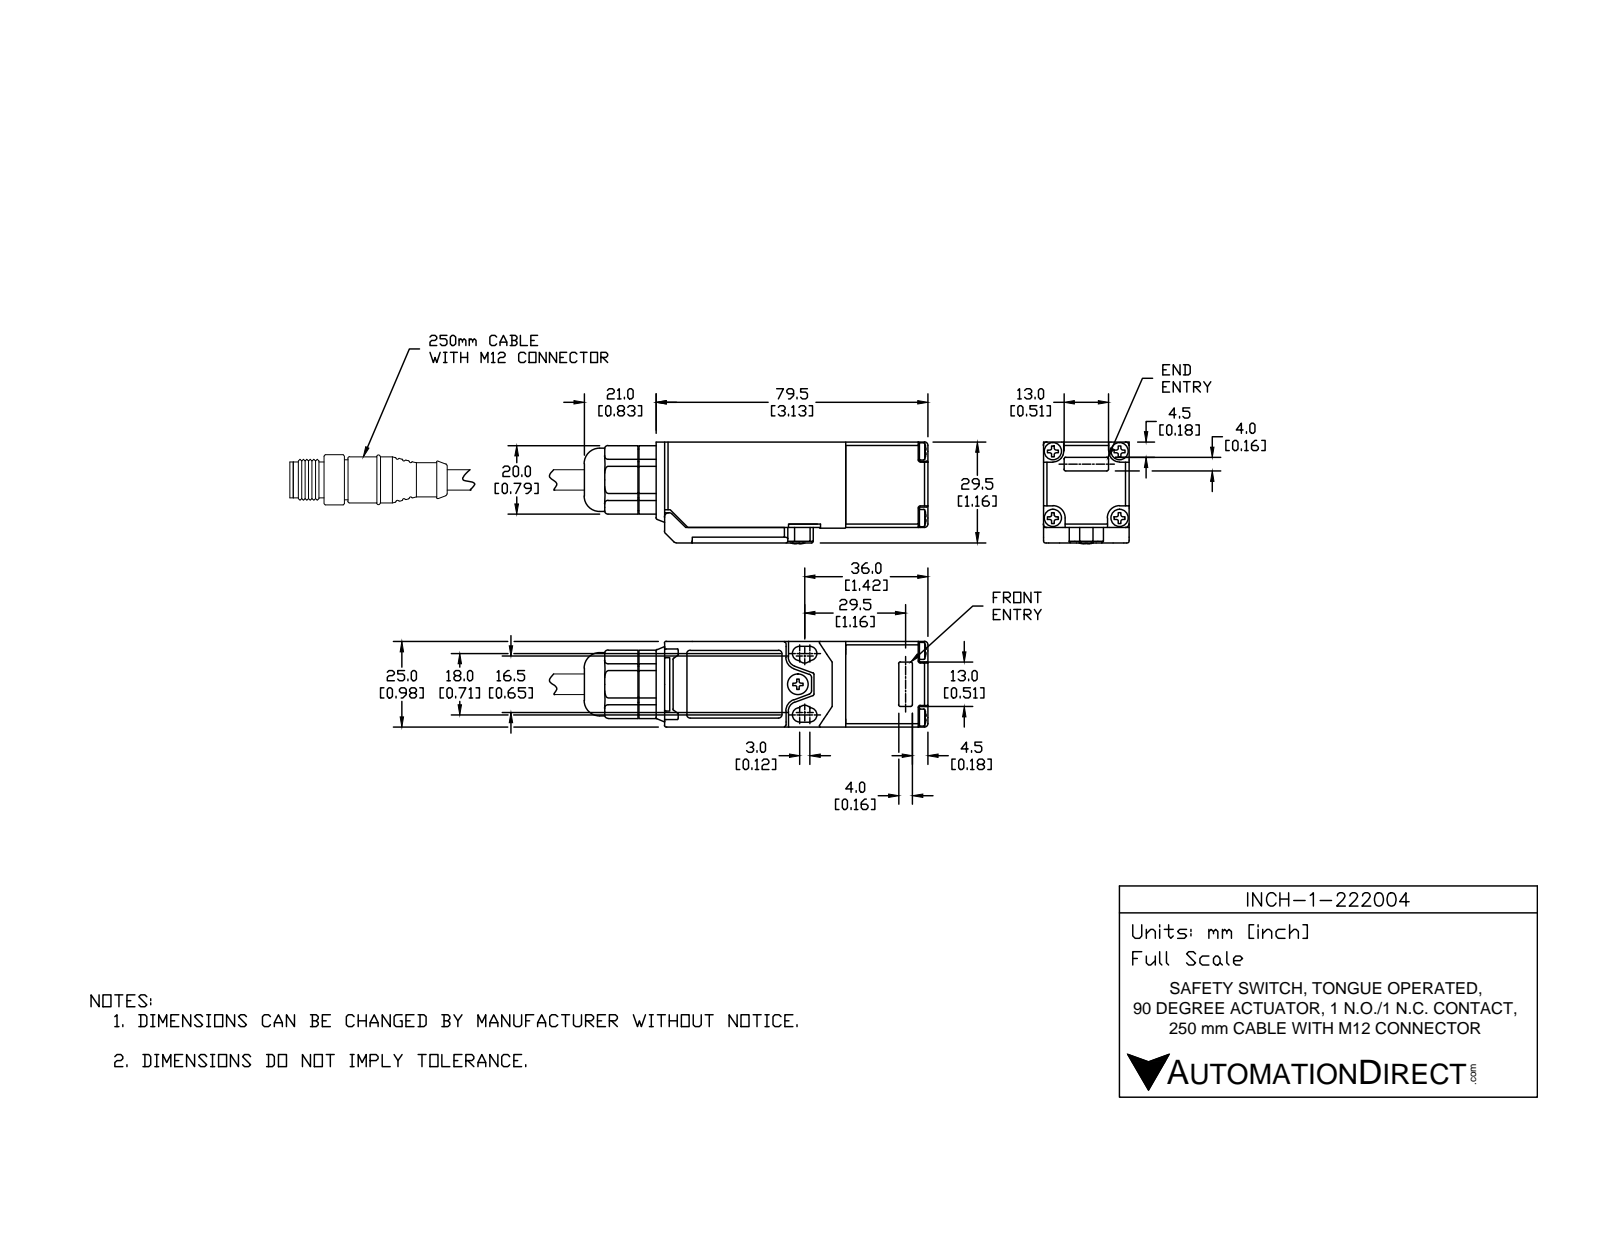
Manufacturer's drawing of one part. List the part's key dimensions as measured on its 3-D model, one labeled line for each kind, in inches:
Part name (STEP PRODUCT): INCH-1-222004
STEP written by: SolidWorks 2014 (AUTOMOTIVE_DESIGN)
Units: inches
Bodies: 14 solids, 1863 faces (738 planar, 677 cylindrical, 448 other)
Overall size (bounding box): 3.169 × 1.172 × 0.984
Volume: 1.453 in³ · Surface area: 40.72 in²
Round holes (diameter × count): ⌀0.126 ×5, ⌀0.094 ×4, ⌀0.059 ×2, ⌀0.063 ×2, ⌀0.071 ×2, ⌀0.087 ×2, ⌀0.142 ×2, ⌀0.055 ×1, ⌀0.098 ×1, ⌀0.102 ×1, ⌀0.197 ×1, ⌀0.217 ×1
Round bosses / shafts (diameter × count): ⌀0.102 ×5, ⌀0.197 ×4, ⌀0.079 ×4, ⌀0.138 ×2, ⌀0.74 ×1, ⌀0.531 ×1, ⌀0.213 ×1, ⌀0.118 ×1
Partial cylindrical surfaces — rounded edges, fillets, slot ends (radius × count): R0.02 ×236, R0.012 ×85, R0.004 ×24, R0.039 ×24, R0.031 ×10, R0.083 ×6, R0.11 ×6, R0.008 ×4
Main face-to-face distances: 0.984, 0.079, 0.039, 0.906, 0.02, 0.874, 0.024, 0.945, 0.929, 0.913
Hole centre spacings: 0.543, 0.768, 0.171, 0.187, 0.423, 0.426, 0.45, 0.581
